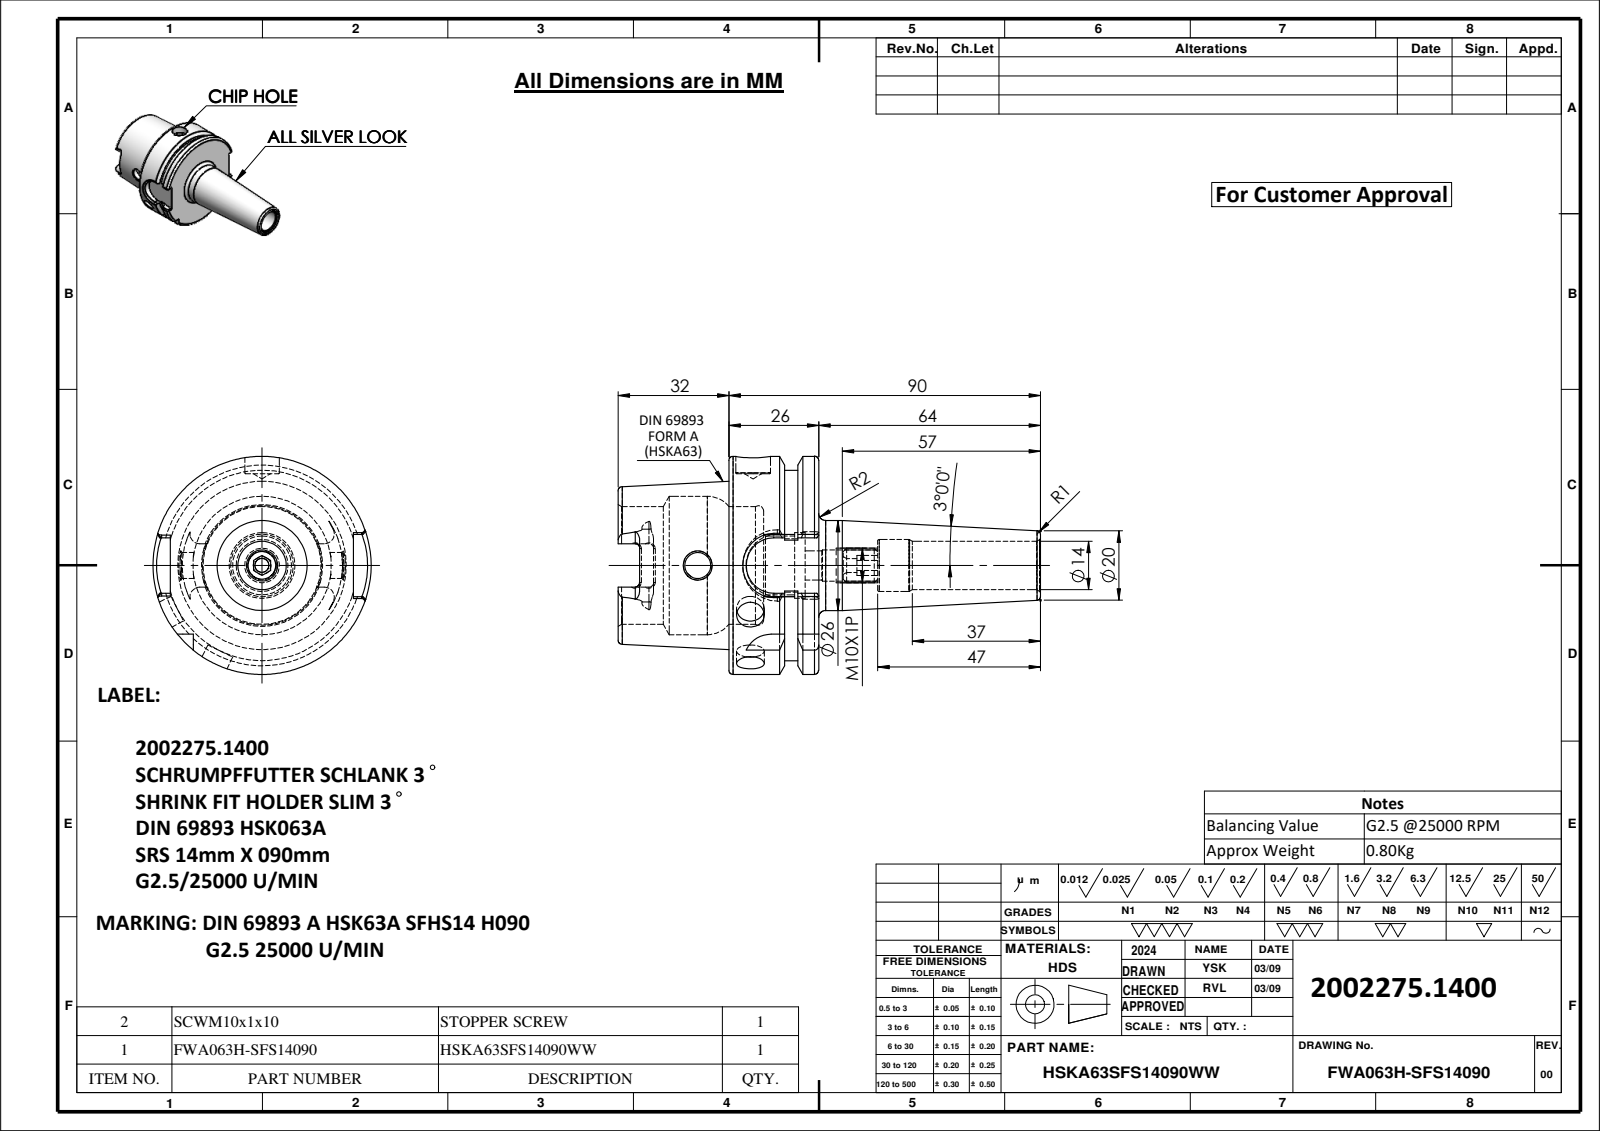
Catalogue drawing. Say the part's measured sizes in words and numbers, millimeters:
The part is named "FWA063H-SFS14090; HSKA63SFS14090WW; SCWM10X1-10". Its 3-D file was written by "SolidWorks 2024 (CONFIG_CONTROL_DESIGN)". It is 2 solids with 196 faces: 59 planar, 57 cylindrical and 80 other. Overall it measures 122 by 63 by 63 millimeters. Its volume is 100 431 cubic millimeters and its surface area 29 856 square millimeters. Round holes: 2 of diameter 8, 1 of diameter 4, 1 of diameter 7.5, 1 of diameter 8.4, 1 of diameter 9, 1 of diameter 10, 1 of diameter 14, 1 of diameter 15, 1 of diameter 17, 1 of diameter 19, 1 of diameter 34, 1 of diameter 40. Round bosses or shafts: 1 of diameter 63, 1 of diameter 55, 1 of diameter 26, 1 of diameter 10. Partial cylindrical surfaces (rounded edges, fillets, slot ends): 6 of radius 1.3, 4 of radius 2.88, 2 of radius 8, 1 of radius 9. The main face-to-face distances are 25.95, 10, 15.95, 32, 42, 57.95, 52.9, 54, 22, 12.
